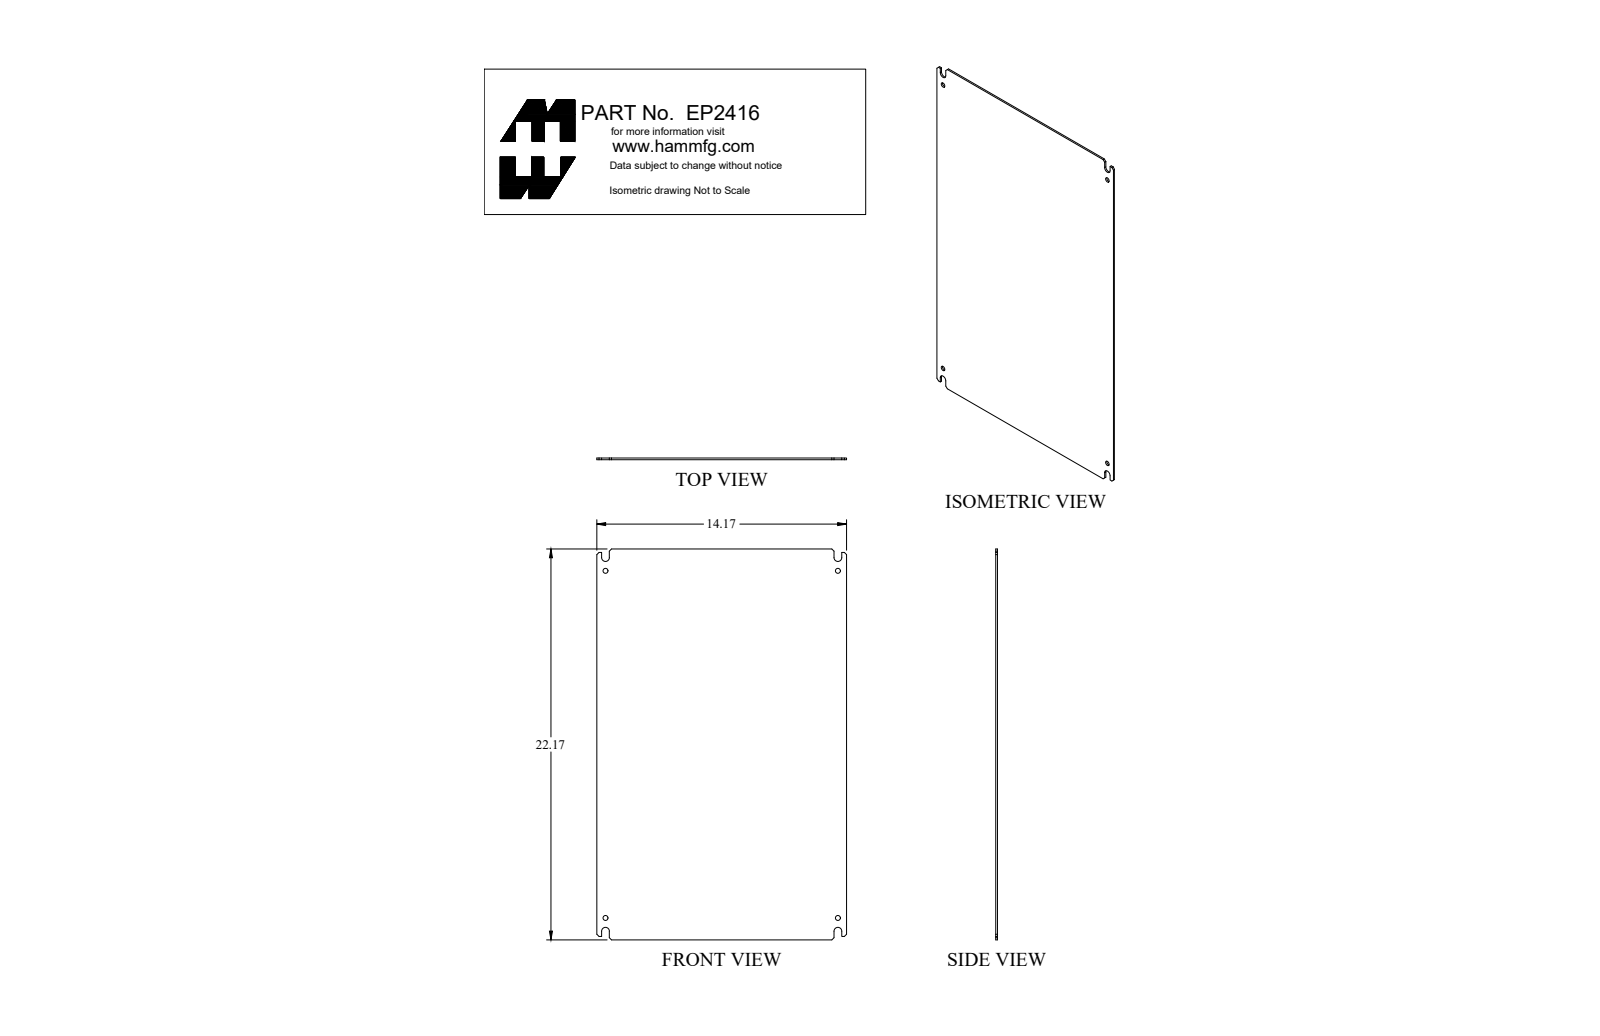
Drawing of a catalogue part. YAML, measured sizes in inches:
part_name: "EP2416"
step_written_by: "SolidWorks 2018 (AUTOMOTIVE_DESIGN)"
units: inches
bodies: {solids: 1, faces: 40, planar: 26, cylindrical: 14, other: 0}
overall_size: [22.17, 14.17, 0.095]
volume: 29.68
surface_area: 632.4
round_holes:
  - {diameter: 0.281, count: 4}
partial_cylinders:
  - {radius: 0.219, count: 4}
face_to_face_distances: [0.095, 14.17, 22.17, 0.709, 13.461, 0.272, 13.898, 0.437, 13.188, 12.751]
hole_center_spacings: [13.188, 19.688, 23.697]
